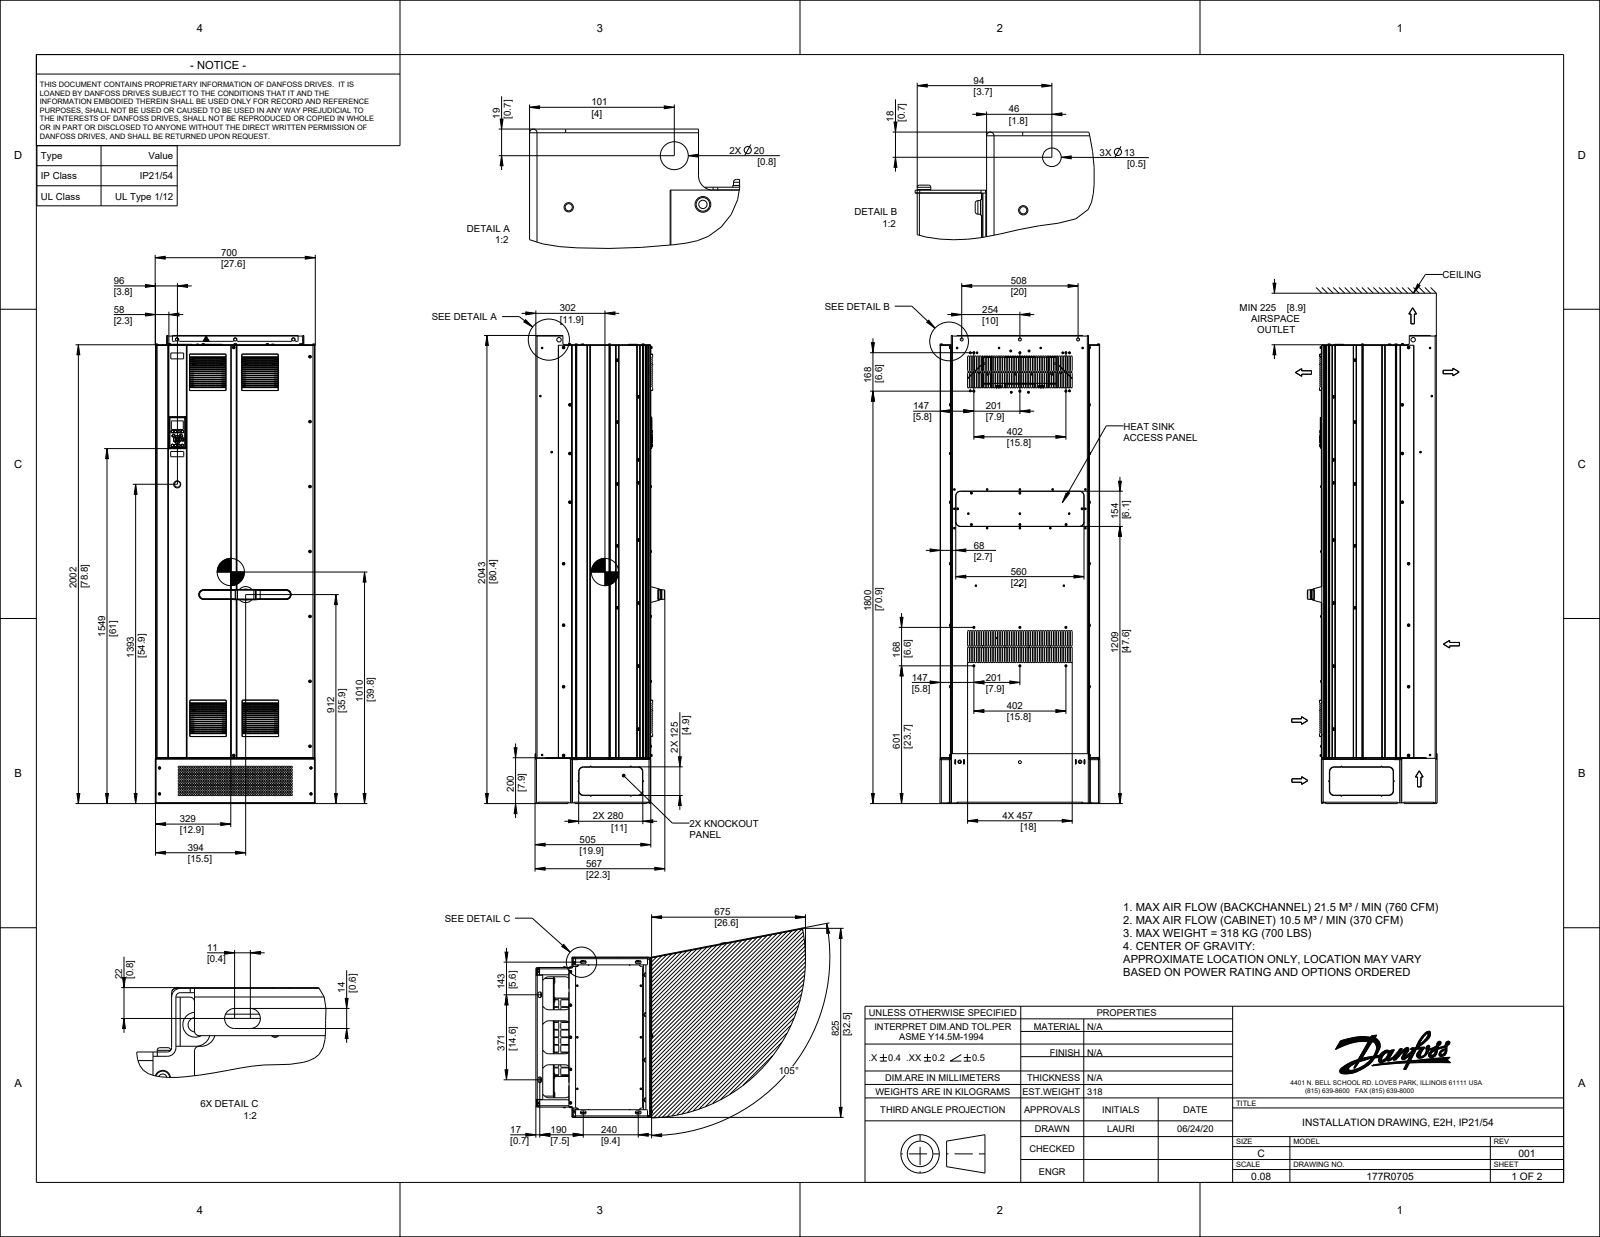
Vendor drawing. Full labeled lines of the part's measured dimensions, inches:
Part name (STEP PRODUCT): 177G8944; FH-M6-15-ZI; SS-M5-2-ZI; S-M6-2-ZI (+8 more)
STEP written by: CREO PARAMETRIC BY PTC INC, 2015480 (CONFIG_CONTROL_DESIGN)
Units: inches
Bodies: 611 solids, 39742 faces (23582 planar, 9167 cylindrical, 6993 other)
Overall size (bounding box): 80.417 × 27.52 × 20.242
Volume: 1 447 in³ · Surface area: 29 250 in²
Round holes (diameter × count): ⌀0.197 ×153, ⌀0.236 ×97, ⌀0.249 ×40, ⌀0.047 ×32, ⌀0.228 ×30, ⌀0.315 ×26, ⌀0.256 ×21, ⌀0.157 ×20, ⌀0.248 ×20, ⌀0.217 ×17, ⌀0.059 ×16, ⌀0.252 ×16
Round bosses / shafts (diameter × count): ⌀0.256 ×85, ⌀0.343 ×62, ⌀0.425 ×52, ⌀0.386 ×52, ⌀0.472 ×46, ⌀0.197 ×34, ⌀0.433 ×26, ⌀0.249 ×22
Partial cylindrical surfaces — rounded edges, fillets, slot ends (radius × count): R0.157 ×456, R0.02 ×369, R0.126 ×323, R0.039 ×243, R0.016 ×139, R0.012 ×130, R0.063 ×105, R0.079 ×86
Main face-to-face distances: 0.118, 0.102, 0.075, 27.287, 19.683, 19.581, 0.091, 0.119, 0.252, 27.035
Hole centre spacings: 5.283, 3.78, 4.08, 7.909, 10.303, 47.843, 1.535, 6.602
